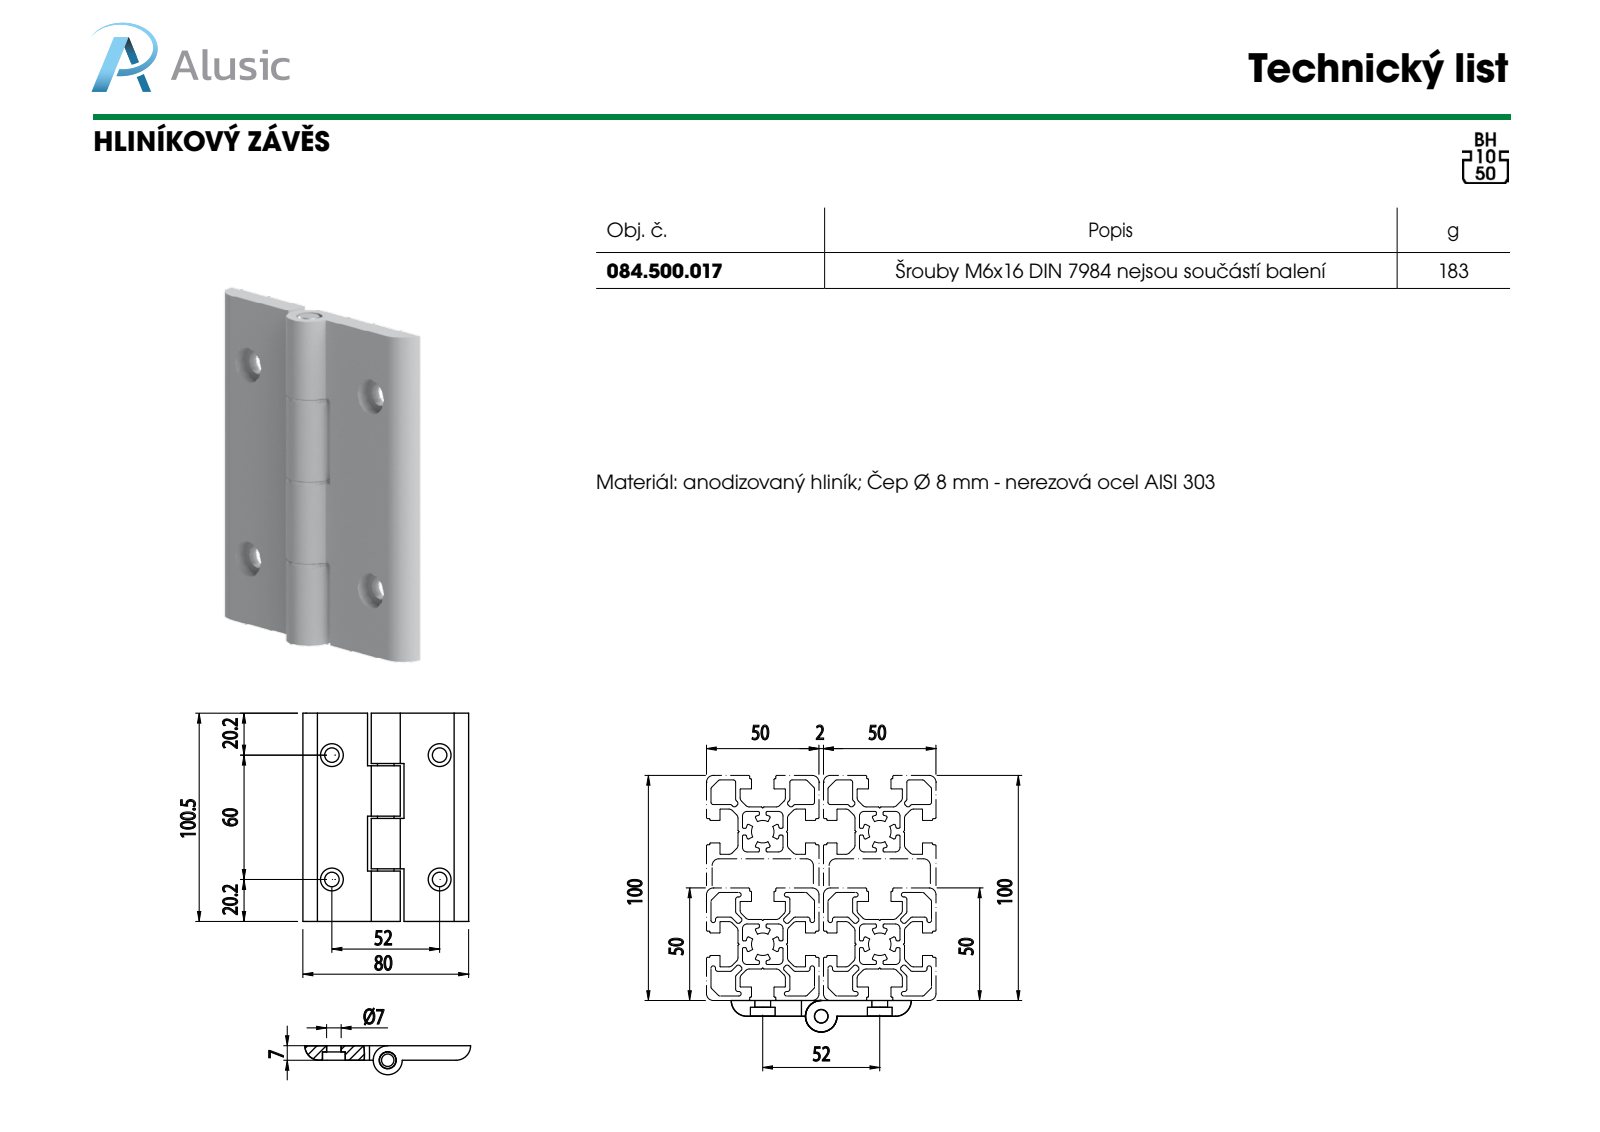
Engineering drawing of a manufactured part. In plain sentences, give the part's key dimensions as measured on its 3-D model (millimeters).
The part is named "084.500.017; 084.500.001.C; PERNO CERNIERA_084.500.004.B; SEMI CERNIERA_084.500.017A". Its 3-D file was written by "SolidWorks 2012 (CONFIG_CONTROL_DESIGN)". It is 6 solids with 200 faces: 150 planar, 46 cylindrical and 4 other. Overall it measures 100.5 by 81 by 14.1 millimeters. Its volume is 57 892 cubic millimeters and its surface area 26 821 square millimeters. Round holes: 4 of diameter 7, 4 of diameter 11, 1 of diameter 8.1, 1 of diameter 8.2. Round bosses or shafts: 1 of diameter 14.1, 1 of diameter 14, 1 of diameter 8. Partial cylindrical surfaces (rounded edges, fillets, slot ends): 2 of radius 7. The main face-to-face distances are 7, 25.4, 50.8, 24.3, 49.7, 100.5, 75.1, 1.1, 17.6, 24.4. The hole center spacings are 52, 60, 79.4.
